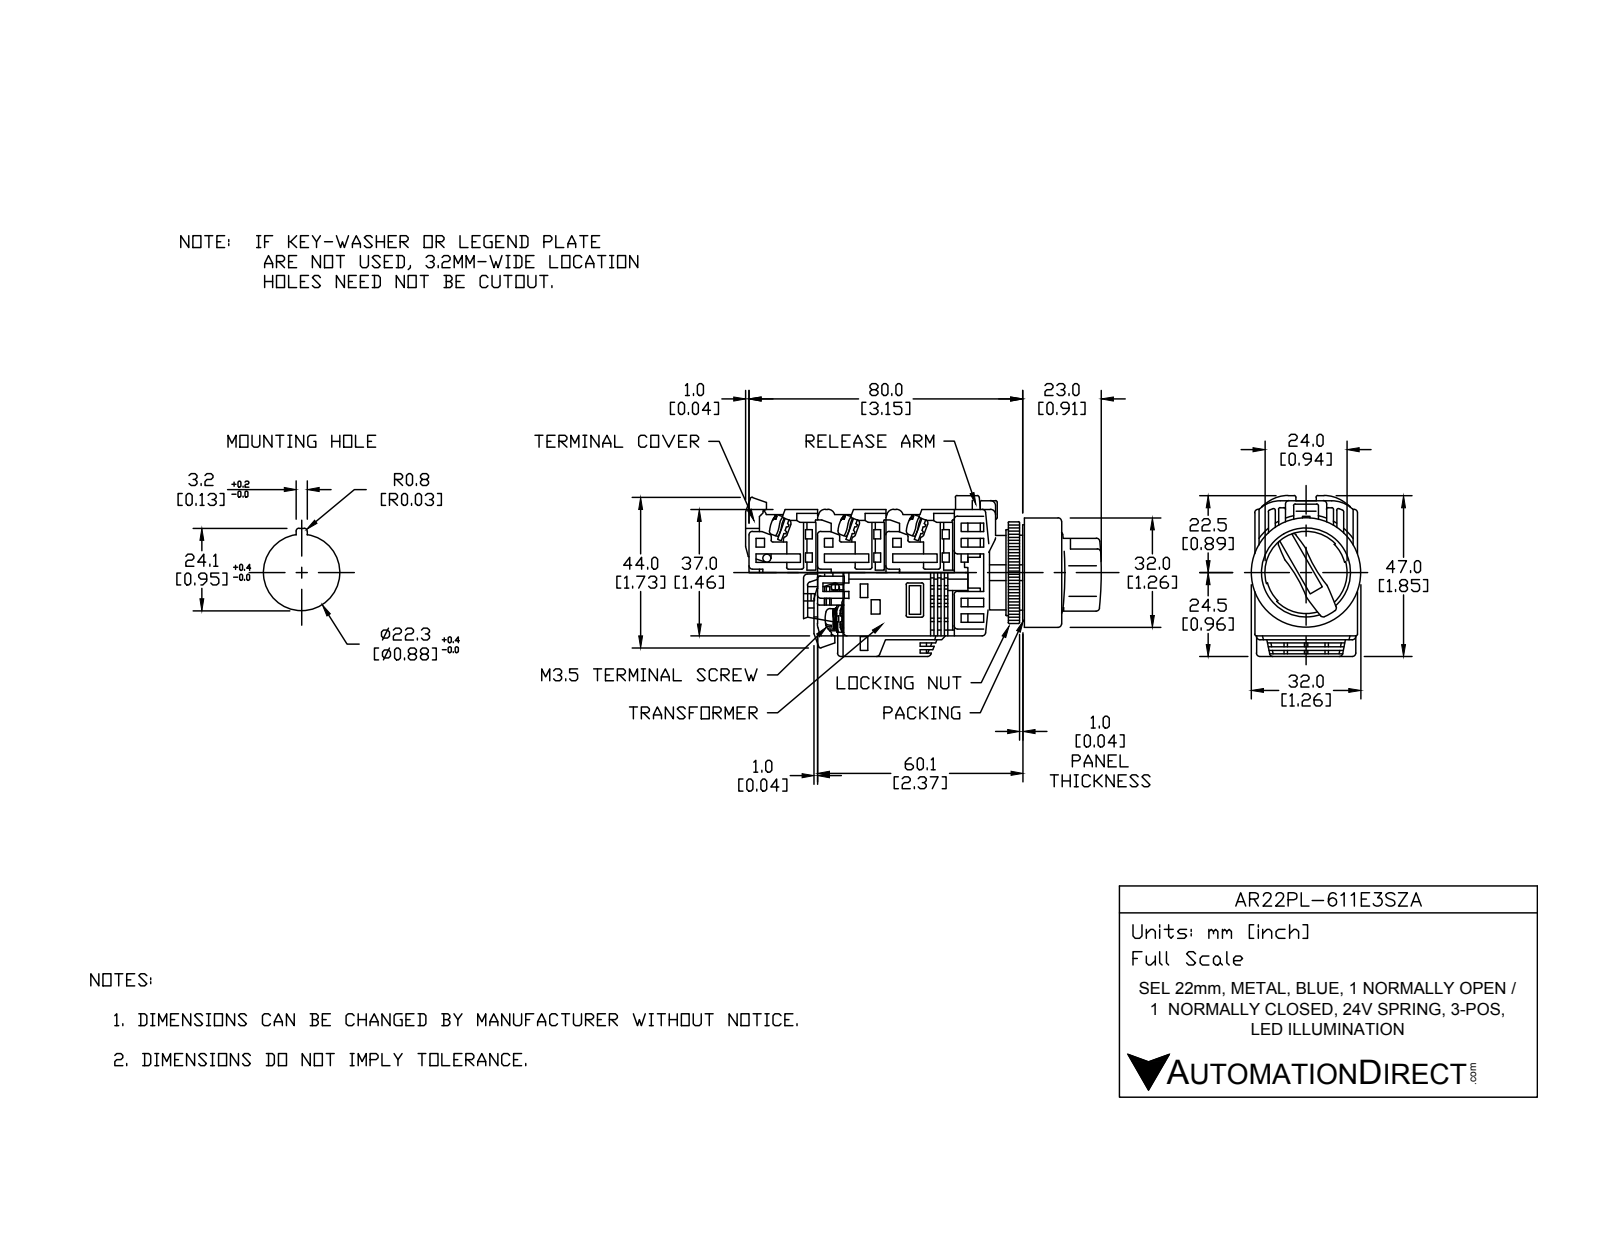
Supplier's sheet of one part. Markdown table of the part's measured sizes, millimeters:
| quantity | value |
| --- | --- |
| part name | AR22PL-611E3SZA |
| STEP written by | SolidWorks 2017 (AUTOMOTIVE_DESIGN) |
| units | millimeters |
| bodies | 23 solids, 556 faces (386 planar, 139 cylindrical, 31 other) |
| overall size | 84.5 × 43.81 × 32 |
| volume | 47 063 mm³ |
| surface area | 28 339 mm² |
| round holes (diameter × count) | 21.8 × 1, 22 × 1, 25 × 1, 31 × 1 |
| round bosses / shafts (diameter × count) | 5 × 6, 32 × 1, 30.5 × 1, 29.8 × 1, 24 × 1, 21.75 × 1, 17 × 1 |
| partial cylindrical surfaces (radius × count) | 0.5 × 48, 1.75 × 8, 1 × 6, 5 × 4, 4 × 2, 12 × 1, 16.59 × 1, 17.59 × 1 |
| main face-to-face distances | 1, 20, 18, 3, 29, 28.5, 48.5, 2, 10, 0.5 |
